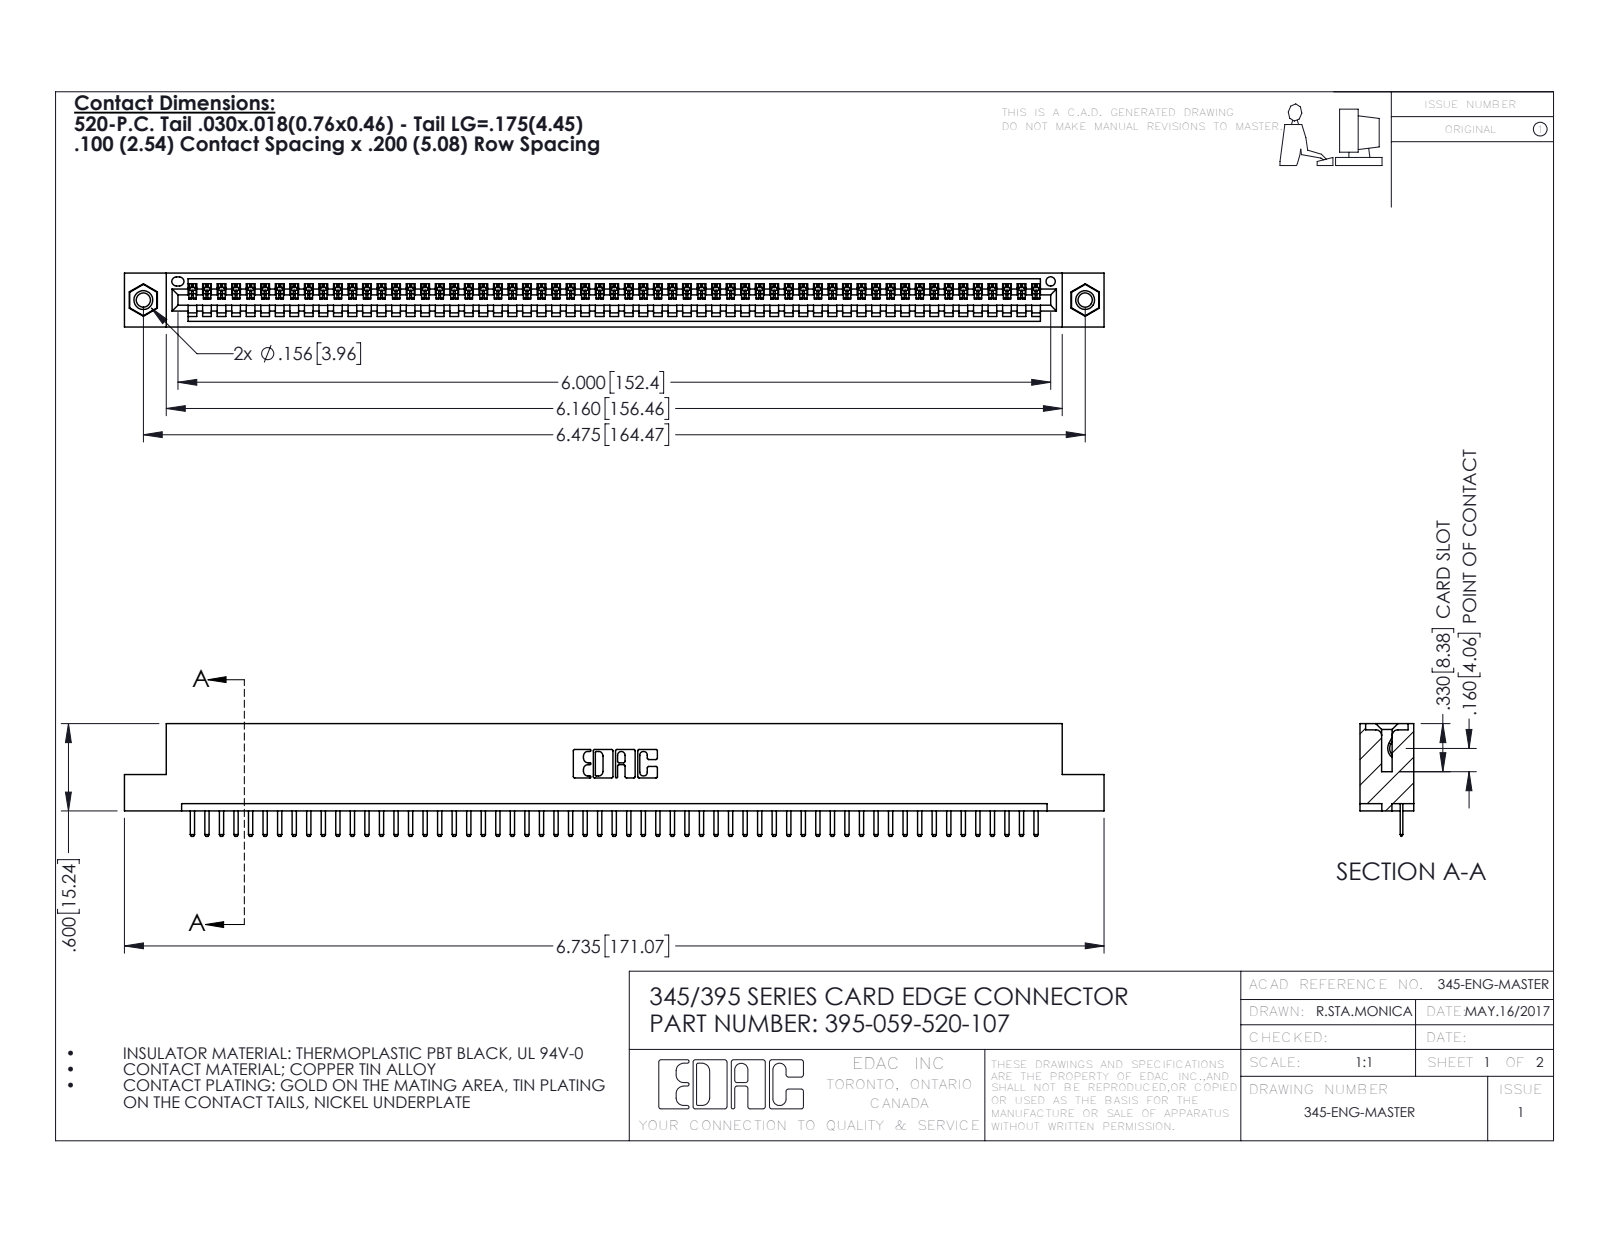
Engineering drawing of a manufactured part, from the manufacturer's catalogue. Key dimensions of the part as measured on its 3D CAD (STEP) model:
Part name (STEP PRODUCT): 345 Part_Flush Mounting Lugs - 0.156 Dia-TI; 345-250-001_345-250-005-103; 345-292-001_345-293-120; 395-059-520-107
STEP written by: SolidWorks 2016 (CONFIG_CONTROL_DESIGN)
Units: inches
Bodies: 62 solids, 3844 faces (2590 planar, 1238 cylindrical, 16 other)
Overall size (bounding box): 6.735 × 0.775 × 0.37
Volume: 0.989 in³ · Surface area: 32.93 in²
Round holes (diameter × count): ⌀0.098 ×2, ⌀0.125 ×2, ⌀0.156 ×2, ⌀0.064 ×1
Round bosses / shafts (diameter × count): ⌀0.155 ×2
Partial cylindrical surfaces — rounded edges, fillets, slot ends (radius × count): R0.01 ×120, R0.006 ×118, R0.01 ×22, R0.007 ×6, R0.031 ×6, R0.026 ×3, R0.031 ×2, R0.04 ×2
Main face-to-face distances: 0.072, 0.298, 0.37, 0.2, 0.098, 0.272, 0.025, 0.225, 0.072, 0.149
Hole centre spacings: 0.27, 6.239, 6.475
